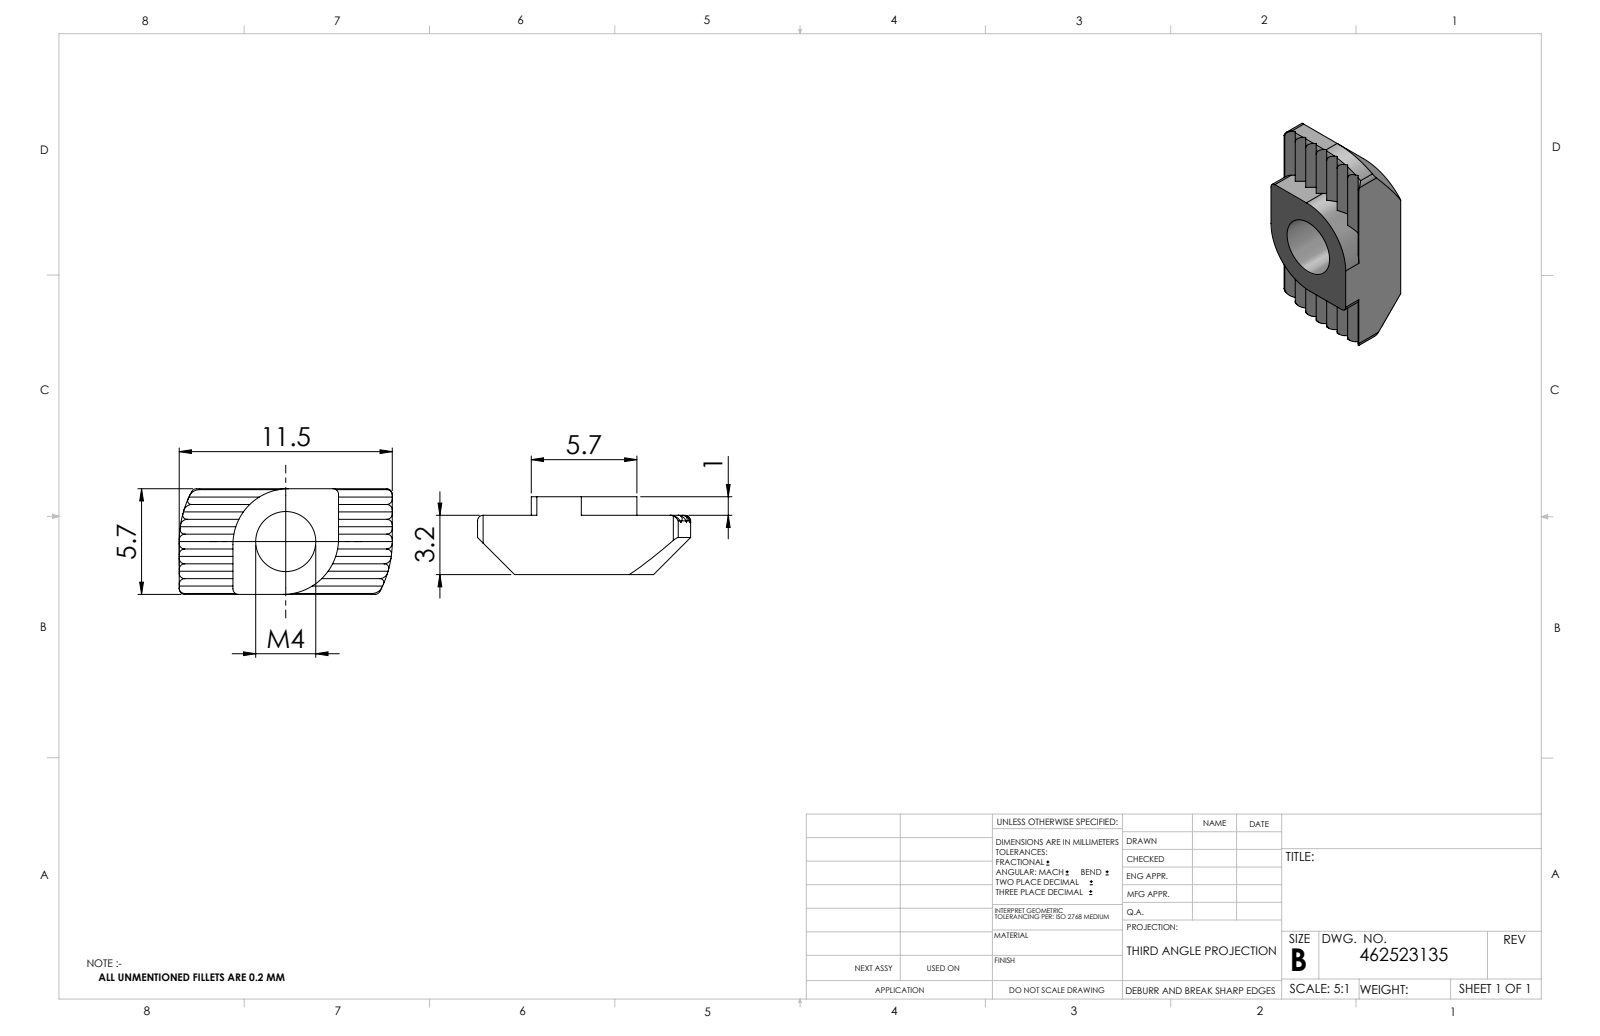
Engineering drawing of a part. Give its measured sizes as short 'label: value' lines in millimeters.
name: 462523135_c_1
written by: SolidWorks 2014 (CONFIG_CONTROL_DESIGN)
unit: mm
bodies: 1 solid, 72 faces (42 planar, 20 cylindrical, 10 other)
size: 11.5 × 5.7 × 4.2
volume: 169 mm³; area: 272 mm²
holes: 1× ⌀3.24
rounds: 8× R0.3, 2× R3, 1× R5.75
face distances: 5.7, 1.13, 4.2, 0.57, 2.26, 0.56, 1.7, 1.69, 3.39, 2.82
